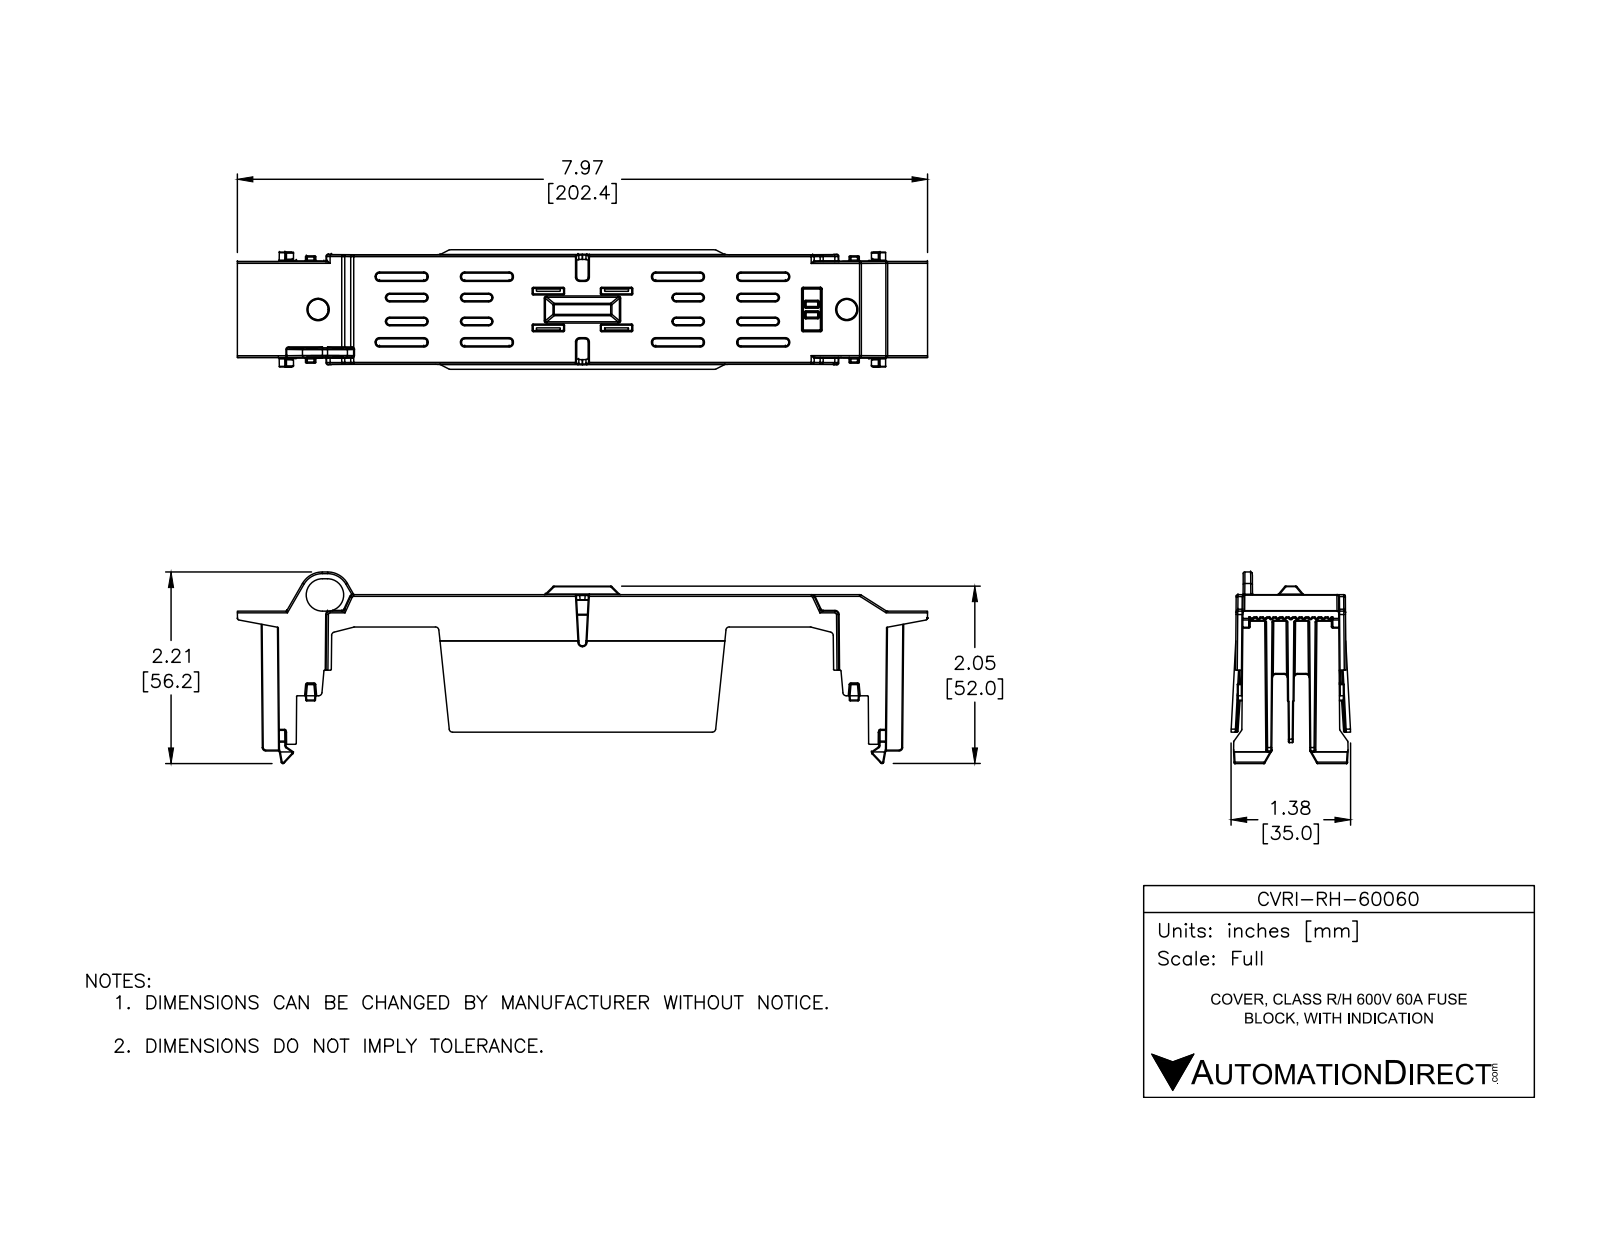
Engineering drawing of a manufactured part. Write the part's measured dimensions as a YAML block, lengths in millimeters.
part_name: "CVRI-RH-60060"
step_written_by: "SolidWorks 2016 (AUTOMOTIVE_DESIGN)"
units: millimeters
bodies: {solids: 1, faces: 2823, planar: 515, cylindrical: 1271, other: 1037}
overall_size: [202.4, 56.2, 35.1]
volume: 30690
surface_area: 40550
partial_cylinders:
  - {radius: 0.3, count: 402}
  - {radius: 0.2, count: 259}
  - {radius: 1, count: 100}
  - {radius: 0.5, count: 61}
  - {radius: 1.2, count: 20}
  - {radius: 0.8, count: 4}
  - {radius: 1.8, count: 4}
  - {radius: 2.5, count: 4}
face_to_face_distances: [1.5, 1.5, 2, 0.5, 3.5, 4.9, 176.1, 3.4, 6.2, 7.3]
